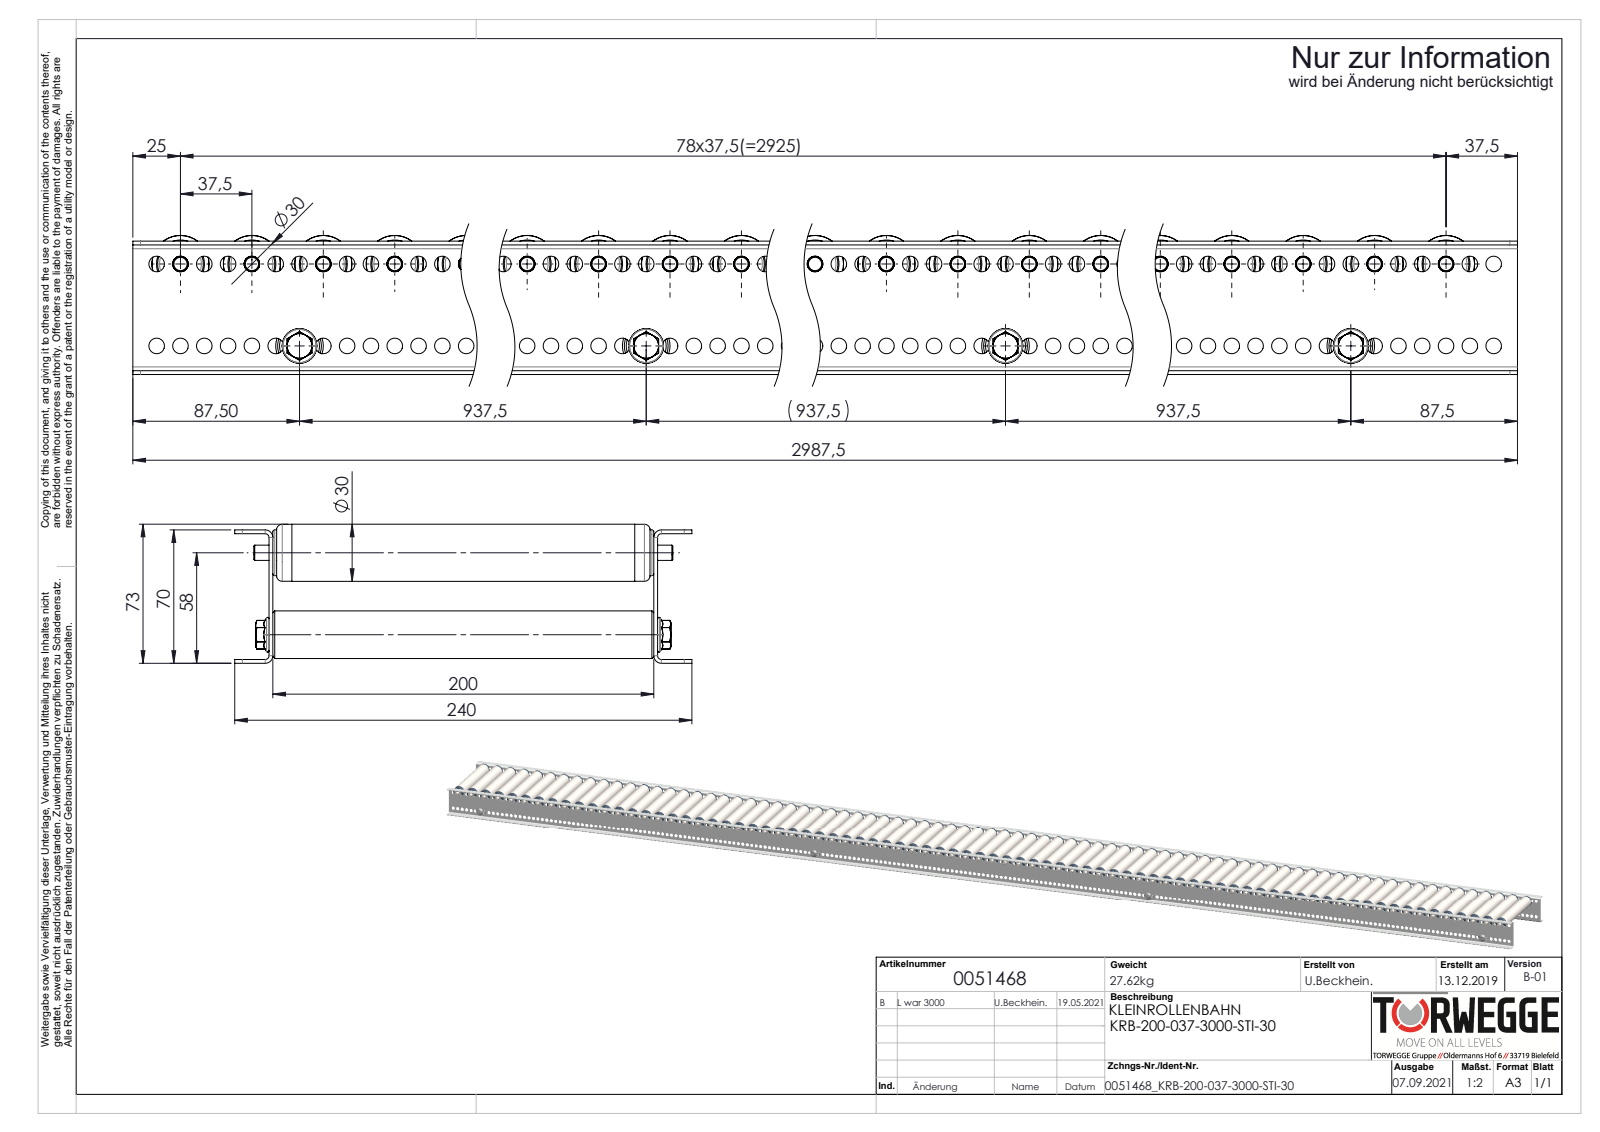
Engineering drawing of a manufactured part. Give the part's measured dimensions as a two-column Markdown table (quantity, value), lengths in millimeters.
| quantity | value |
| --- | --- |
| part name | 0024176_Passscheibe_DIN988_8x14x1; Traversen_KFG_L200; S100994_Sperrzahnschraube_M08x16-8.8-A2K; 0039768_Tragrollenrohr-Ø30x1,5STI_KFG_0039768_L=180 (+6 more) |
| STEP written by | SolidWorks 2020 (AUTOMOTIVE_DESIGN) |
| units | millimeters |
| bodies | 496 solids, 20898 faces (6524 planar, 8320 cylindrical, 6054 other) |
| overall size | 2987.5 × 240 × 73 |
| volume | 4 139 000 mm³ |
| surface area | 5 474 000 mm² |
| round holes (diameter × count) | 8.2 × 476, 8 × 79, 8.1 × 79, 23.2 × 79, 25.2 × 79, 27 × 79, 6.8 × 4, 21 × 4 |
| round bosses / shafts (diameter × count) | 30 × 79, 29.9 × 79, 27.1 × 79, 26.8 × 79, 24 × 79, 14 × 79, 25 × 4, 8 × 4 |
| partial cylindrical surfaces (radius × count) | 5.05 × 79, 4 × 8, 2 × 4 |
| main face-to-face distances | 2, 202, 200, 68, 204, 70, 66, 10, 190, 20 |
| hole center spacings | 12.5, 25, 37.5, 50, 62.5, 75, 87.5, 100 |
